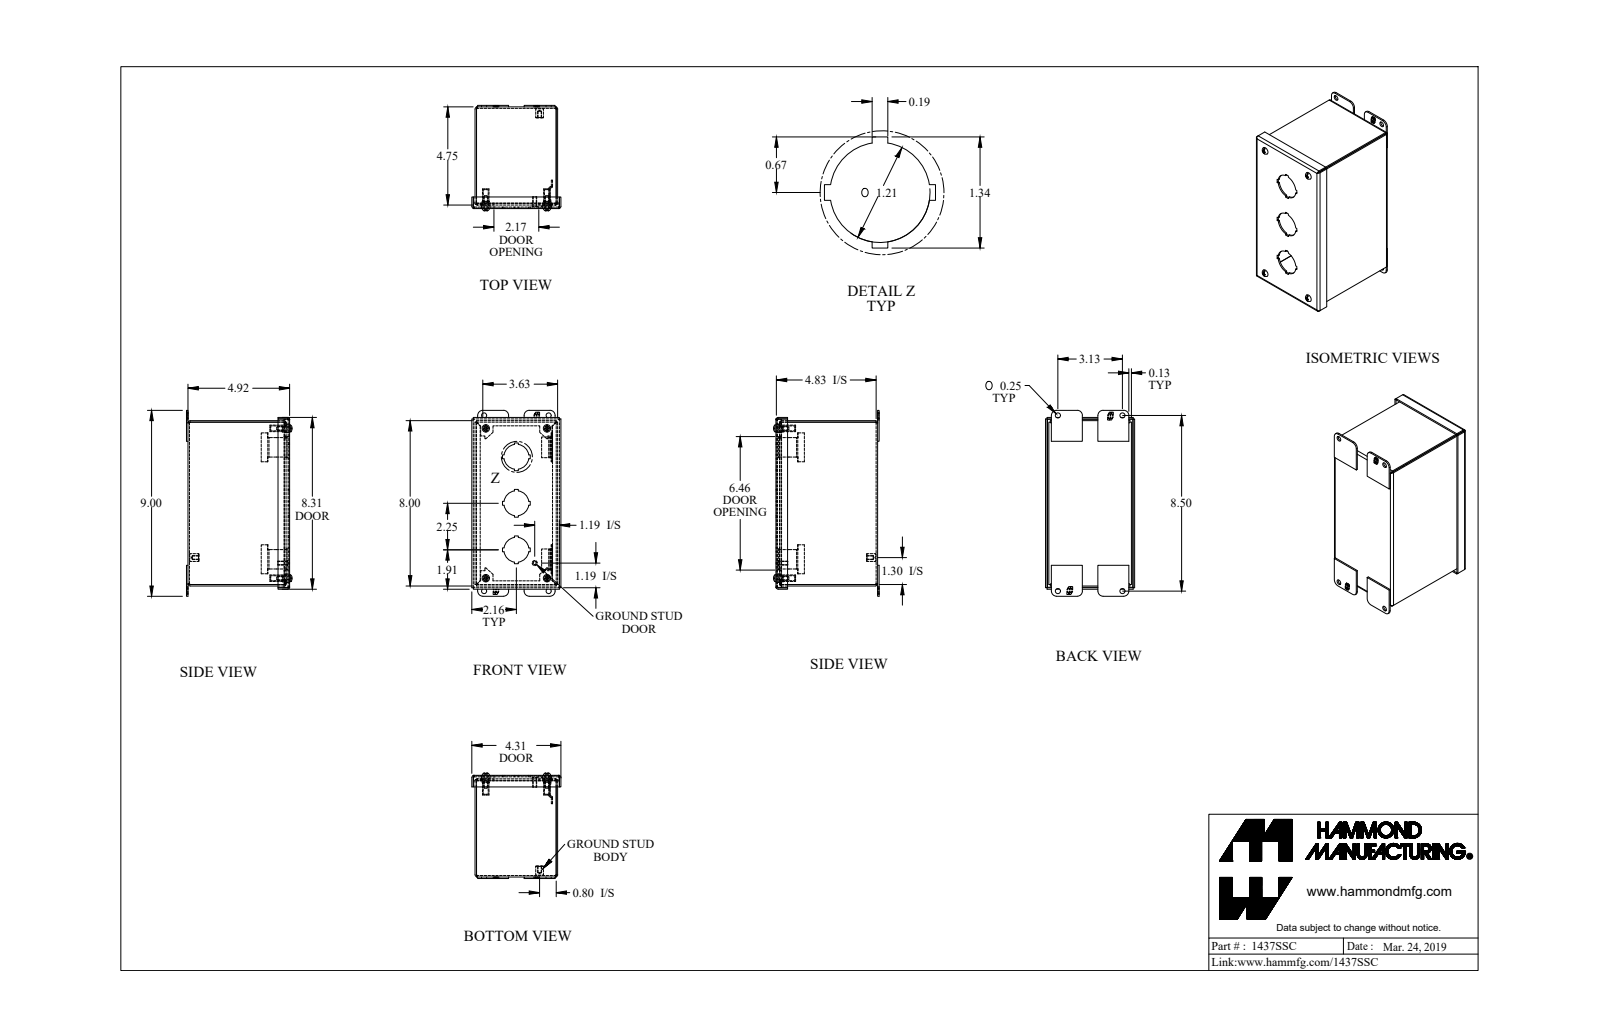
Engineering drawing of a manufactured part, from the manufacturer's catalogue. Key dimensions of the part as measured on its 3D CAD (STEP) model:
Part name (STEP PRODUCT): 1437SSC_Default
STEP written by: SolidWorks 2019 (CONFIG_CONTROL_DESIGN)
Units: inches
Bodies: 23 solids, 653 faces (459 planar, 164 cylindrical, 30 other)
Overall size (bounding box): 9 × 5.104 × 4.312
Volume: 16.98 in³ · Surface area: 454.9 in²
Round holes (diameter × count): ⌀0.25 ×8, ⌀0.065 ×4, ⌀0.239 ×4, ⌀0.253 ×4, ⌀0.406 ×4, ⌀1.21 ×3, ⌀0.156 ×1
Round bosses / shafts (diameter × count): ⌀0.19 ×5, ⌀0.406 ×4, ⌀0.315 ×4, ⌀0.148 ×4, ⌀0.375 ×1, ⌀0.25 ×1
Partial cylindrical surfaces — rounded edges, fillets, slot ends (radius × count): R0.036 ×12, R0.108 ×12, R0.25 ×8, R0.029 ×4, R0.086 ×4, R0.125 ×4, R0.171 ×4
Main face-to-face distances: 0.072, 3.928, 4.85, 4.922, 3.856, 4, 7.928, 4.778, 0.156, 7.856
Hole centre spacings: 7.25, 7.876, 0.63, 2.961, 3.107, 3.916, 6.059, 7.832
